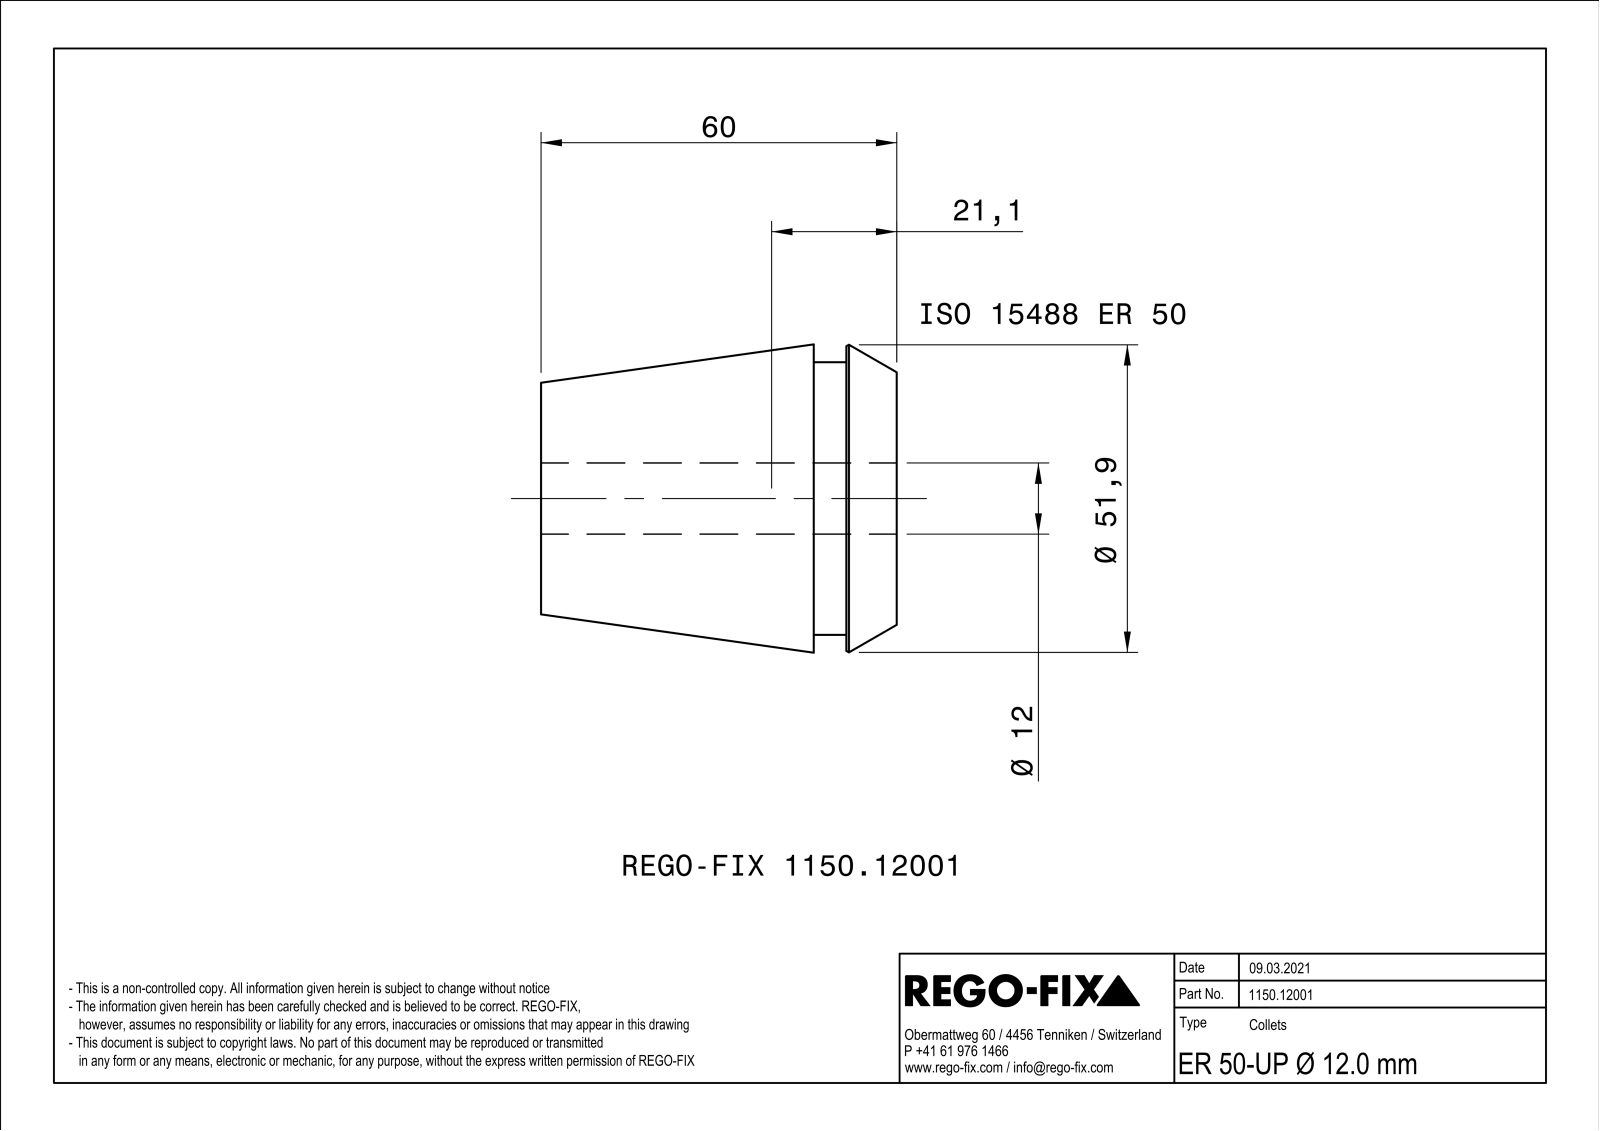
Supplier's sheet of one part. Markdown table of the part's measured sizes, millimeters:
| quantity | value |
| --- | --- |
| part name | NOCUT |
| STEP written by | SIEMENS PLM Software Solid Edge ST10 (AUTOMOTIVE_DESIGN) |
| units | millimeters |
| bodies | 1 solid, 177 faces (88 planar, 9 cylindrical, 80 other) |
| overall size | 60 × 51.99 × 51.99 |
| volume | 78 324 mm³ |
| surface area | 41 675 mm² |
| round holes (diameter × count) | 12 × 1 |
| round bosses / shafts (diameter × count) | 46 × 1 |
| main face-to-face distances | 1, 60, 14, 46, 8.5, 5.5, 51.5, 9, 0.5, 5 |
